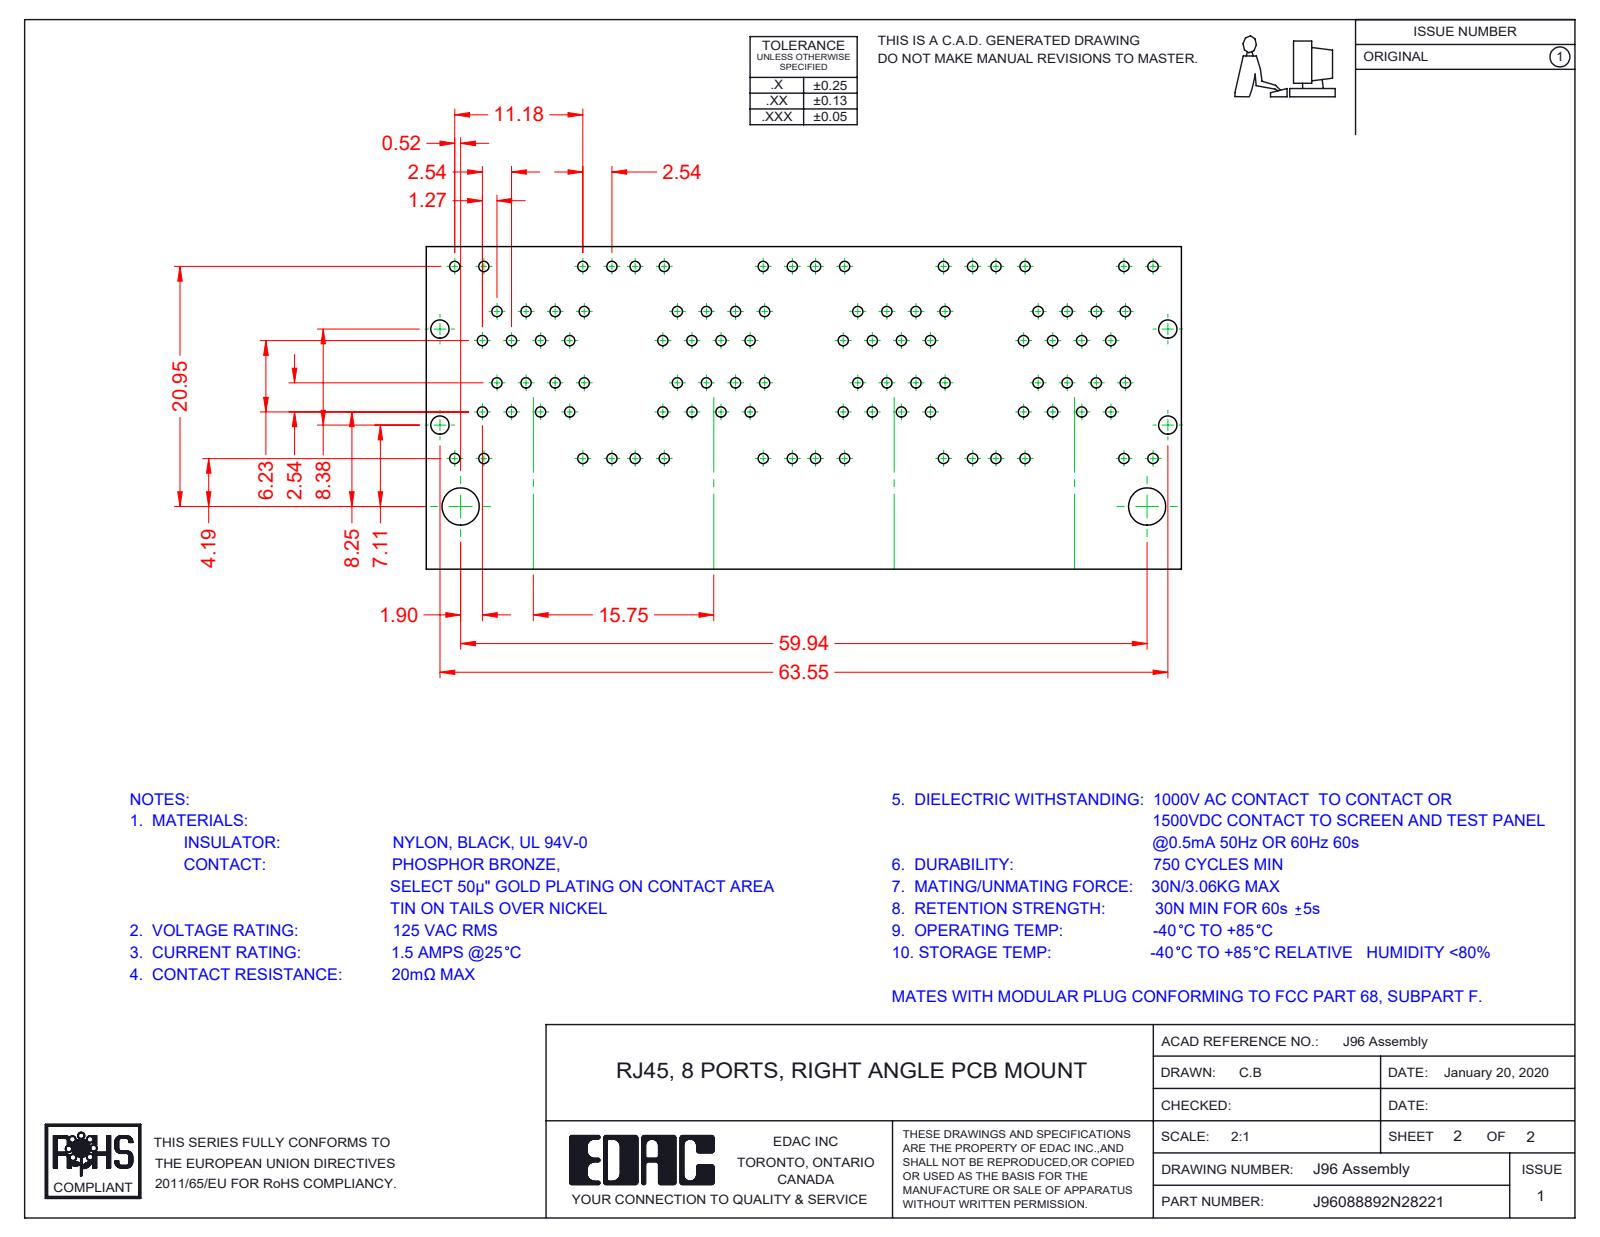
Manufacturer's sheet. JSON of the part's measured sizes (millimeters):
{"part_name": "96 LED LH Upper_2-Red; 96 Contact Lock Upper; 96 Contacts Lower; 96 LED RH Upper_8-Red-Yellow (+8 more)", "step_written_by": "SolidWorks 2016 (CONFIG_CONTROL_DESIGN)", "units": "millimeters", "bodies": {"solids": 96, "faces": 7820, "planar": 6105, "cylindrical": 1404, "other": 311}, "overall_size": [67.35, 31.38, 28.68], "volume_mm3": 24149, "surface_area_mm2": 63596, "round_holes": [[1.7, 3]], "round_bosses_or_shafts": [[1.68, 3]], "partial_cylinders_radius": [[0.25, 124], [0.35, 73], [1, 72], [0.5, 49], [0.91, 32], [0.2, 27], [0.27, 14], [0.7, 11]], "face_to_face_distances": [15.75, 0.35, 9.95, 1.17, 1.6, 0.54, 9.98, 10.18, 12.67, 3.37], "hole_center_spacings": [15.75, 31.5]}
